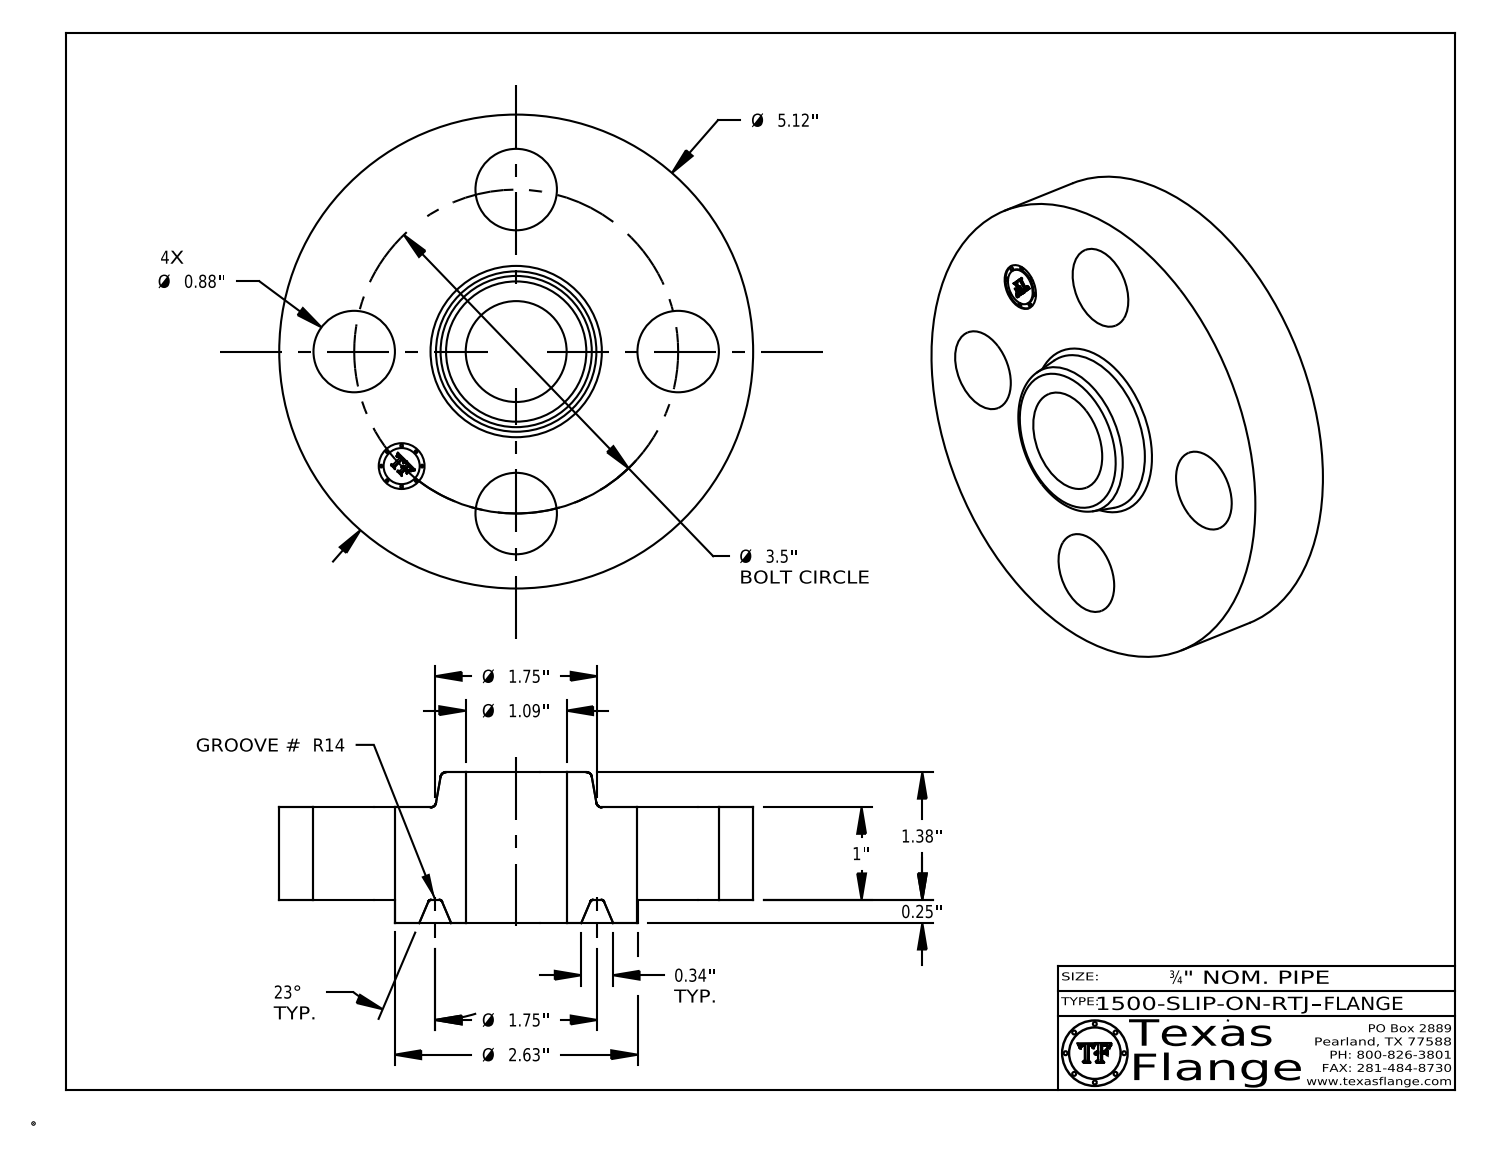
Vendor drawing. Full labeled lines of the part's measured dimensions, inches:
Part name (STEP PRODUCT): 1500-SLIP-ON-RTJ
STEP written by: CATIA V5 STEP AP214 (AUTOMOTIVE_DESIGN)
Units: inches
Bodies: 1 solid, 423 faces (371 planar, 38 cylindrical, 14 other)
Overall size (bounding box): 5.12 × 5.12 × 1.63
Volume: 18.51 in³ · Surface area: 72.6 in²
Round holes (diameter × count): ⌀0.88 ×4, ⌀0.495 ×1, ⌀1.09 ×1
Round bosses / shafts (diameter × count): ⌀0.03 ×8, ⌀5.12 ×1, ⌀2.625 ×1, ⌀0.39 ×1
Main face-to-face distances: 1, 0.25, 1.25, 1.63, 1.38, 0.38, 0.015, 1.235, 0.985, 0.395
Hole centre spacings: 1.75, 2.475, 1.339, 3.233, 3.5
